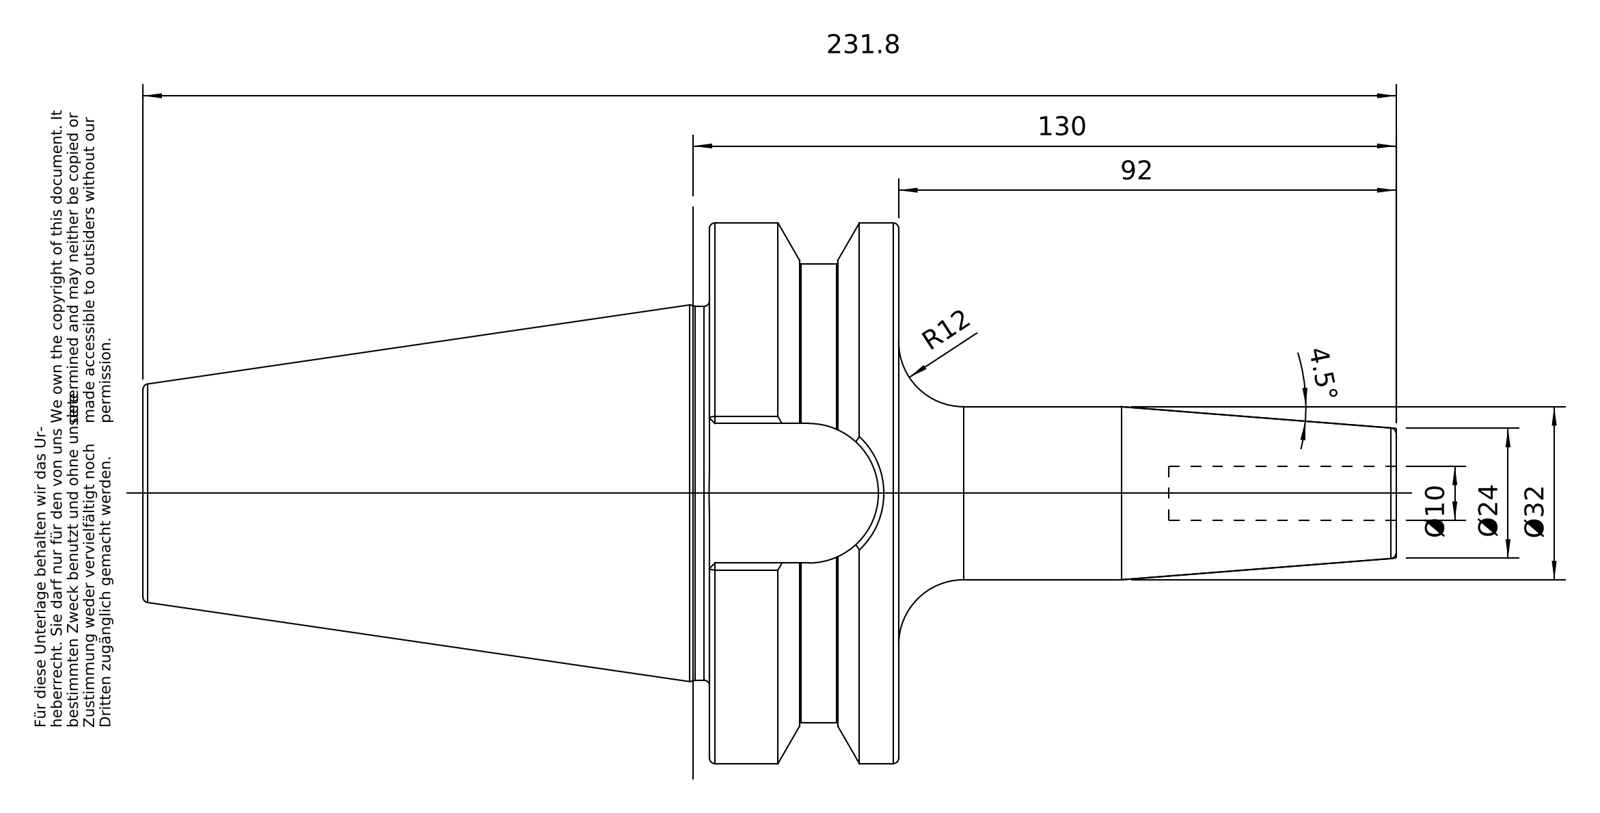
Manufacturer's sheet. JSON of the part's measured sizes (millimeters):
{"part_name": "50-644-10", "step_written_by": "PRO/ENGINEER BY PARAMETRIC TECHNOLOGY CORPORATION, 2010430 (CONFIG_CONTROL_DESIGN)", "units": "millimeters", "bodies": {"solids": 1, "faces": 96, "planar": 26, "cylindrical": 22, "other": 48}, "overall_size": [231.8, 99.97, 99.97], "volume_mm3": 532985, "surface_area_mm2": 60958, "round_holes": [[10, 1], [20.75, 1], [25.02, 1], [25.7, 1]], "round_bosses_or_shafts": [[99.97, 1], [84.75, 1], [69.15, 1], [32, 1], [24.01, 1]], "partial_cylinders_radius": [[12.9, 1]], "face_to_face_distances": [35, 70.4, 104.8, 139.8, 25.8, 231.8, 127, 92, 48, 56.8]}
